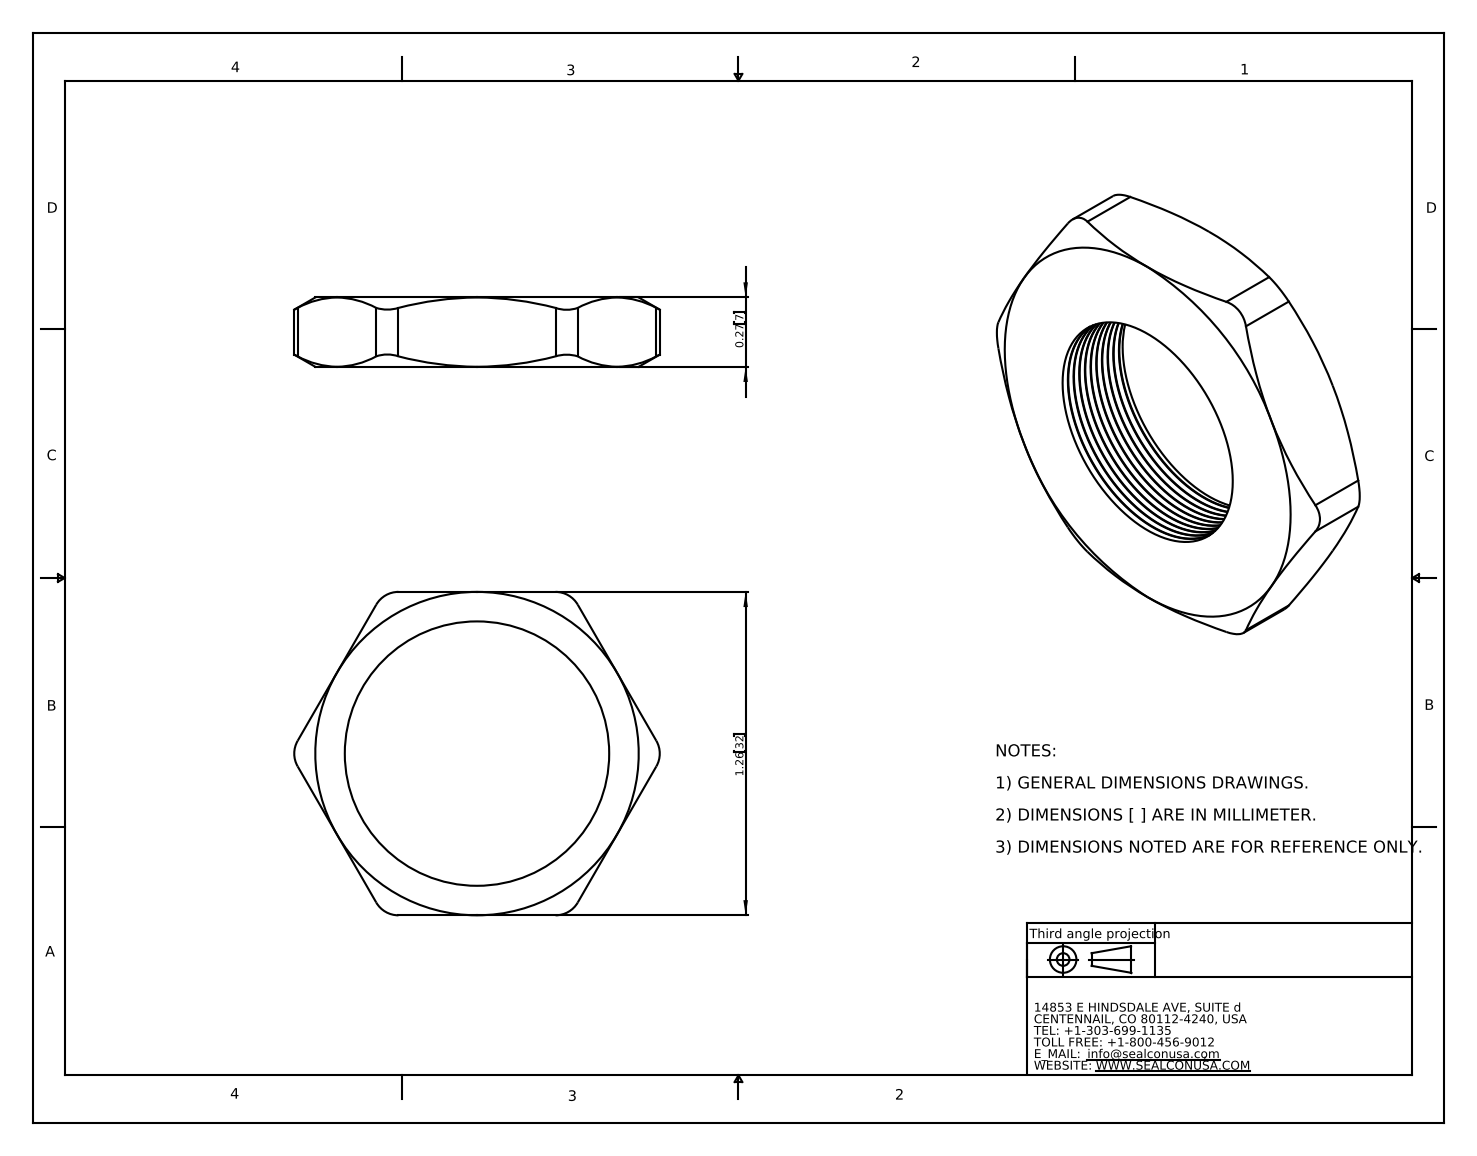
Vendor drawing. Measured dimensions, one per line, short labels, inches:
name: NN-21-BK
written by: SolidWorks 2008 (CONFIG_CONTROL_DESIGN)
unit: in
bodies: 1 solid, 93 faces (8 planar, 27 cylindrical, 58 other)
size: 1.424 × 1.26 × 0.27
volume: 0.241 in³; area: 4.148 in²
holes: 1× ⌀0.75
rounds: 6× R0.1
face distances: 0.27, 1.26
